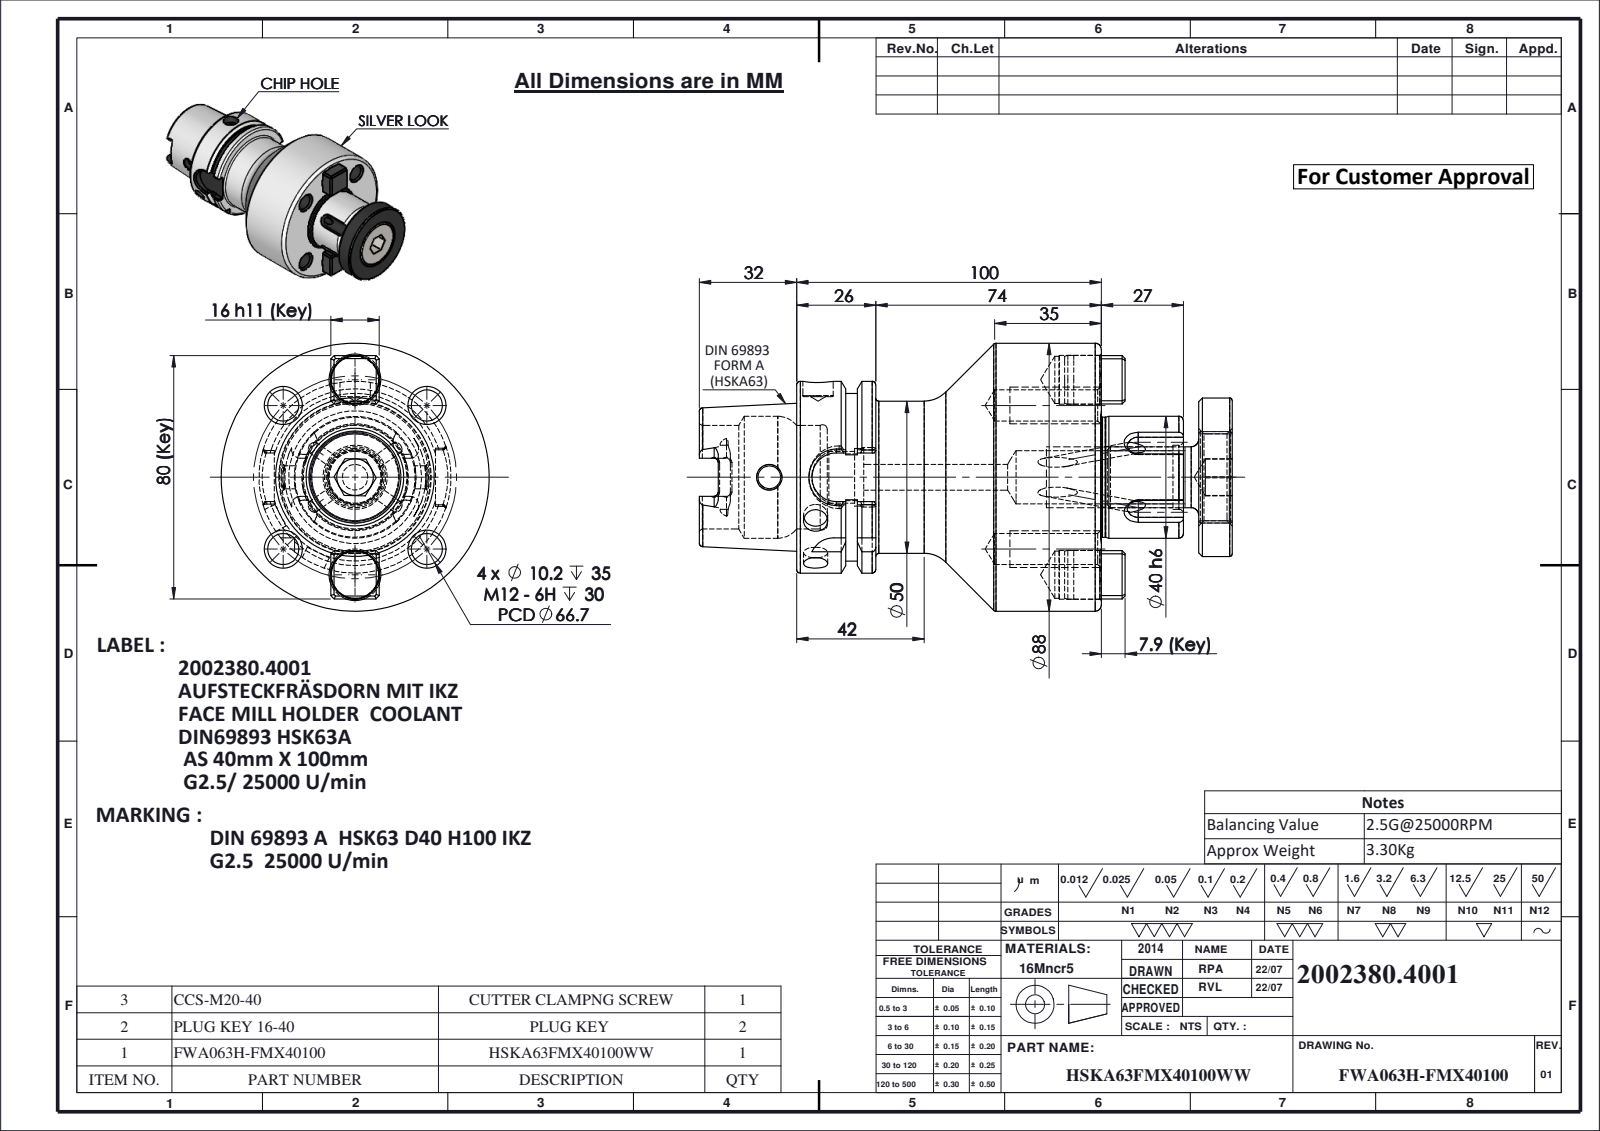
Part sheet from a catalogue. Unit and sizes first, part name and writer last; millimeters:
Units: millimetres
Overall size (bounding box): 175 × 88 × 88
Round holes (diameter × count): ⌀4 ×4, ⌀10.2 ×4, ⌀8 ×2, ⌀15.5 ×2, ⌀16 ×2, ⌀7.5 ×1, ⌀8.4 ×1, ⌀10 ×1, ⌀17 ×1, ⌀17.5 ×1, ⌀19 ×1, ⌀21 ×1
Round bosses / shafts (diameter × count): ⌀16.02 ×2, ⌀16.02 ×2, ⌀88 ×1, ⌀63 ×1, ⌀55 ×1, ⌀52 ×1, ⌀50 ×1, ⌀39.4 ×1
Partial cylindrical surfaces — rounded edges, fillets, slot ends (radius × count): R1.3 ×6, R2.88 ×4, R4 ×4, R8 ×2, R10.5 ×2, R9 ×1
Main face-to-face distances: 43, 32, 132, 11, 100, 143, 12, 25.95, 74.05, 106.05
Hole centre spacings: 33.35, 60.38, 25.04, 25.05, 32, 47.16, 47.17, 66.7
Volume: 442 423 mm³ · Surface area: 72 603 mm²
Bodies: 5 solids, 388 faces (114 planar, 113 cylindrical, 161 other)
Part name (STEP PRODUCT): HSKA63FMX40100WW; CCS-M20-40; CCS-M20-40-1; PLUG KEY 16-40 (+2 more)
STEP written by: SolidWorks 2024 (CONFIG_CONTROL_DESIGN)
